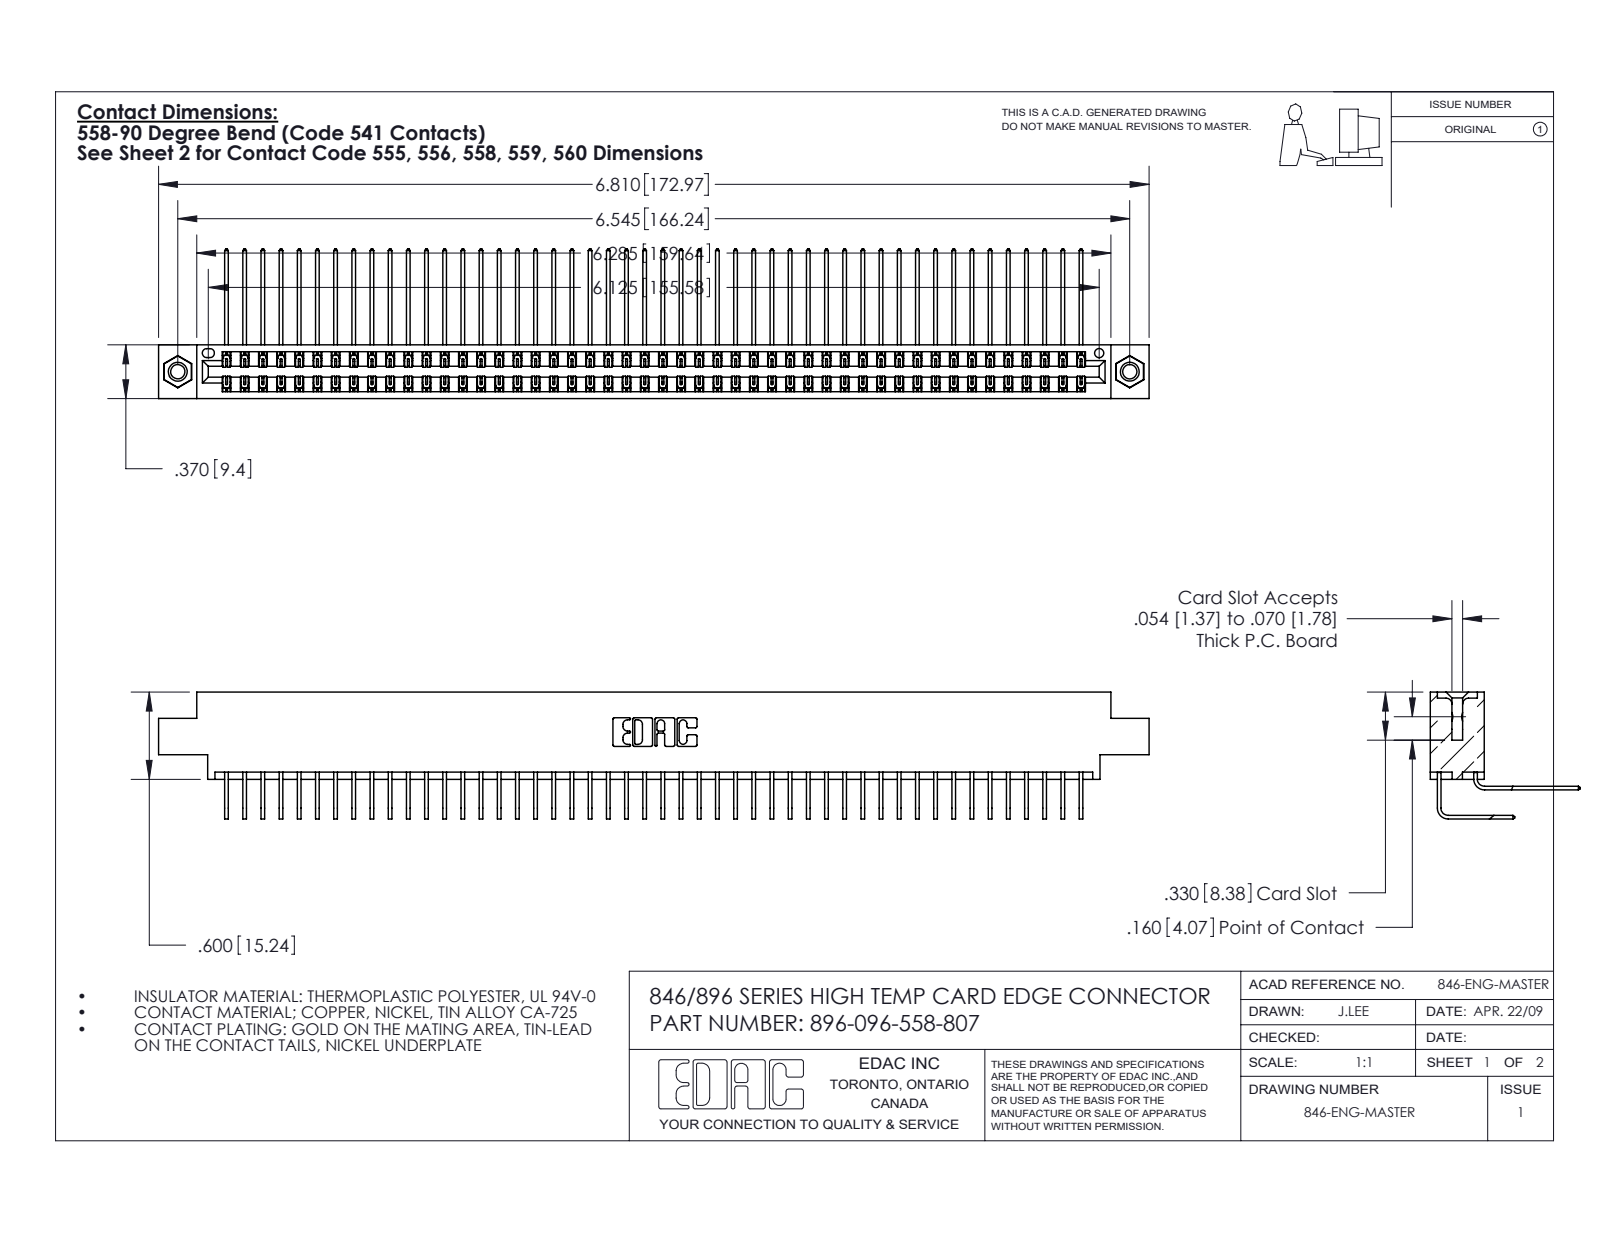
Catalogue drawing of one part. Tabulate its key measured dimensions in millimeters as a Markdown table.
| quantity | value |
| --- | --- |
| part name | 345-250-001_345-250-005-103; 345-292-001_558 Tail - 2; 346 Part_0.170 Offset - 0.156 Dia-TI; 345-292-001_558 559 Tail - 1 (+1 more) |
| STEP written by | SolidWorks 2016 (CONFIG_CONTROL_DESIGN) |
| units | millimeters |
| bodies | 99 solids, 5370 faces (3664 planar, 1690 cylindrical, 16 other) |
| overall size | 173 × 26.2 × 22.2 |
| volume | 17 300 mm³ |
| surface area | 26 740 mm² |
| round holes (diameter × count) | 2.5 × 2, 3.2 × 2, 4 × 2, 1.6 × 1 |
| round bosses / shafts (diameter × count) | 3.9 × 2 |
| partial cylindrical surfaces (radius × count) | 0.2 × 144, 0.3 × 22, 0.2 × 6, 0.8 × 6, 0.7 × 3, 0.4 × 2, 0.6 × 2, 0.6 × 2 |
| main face-to-face distances | 8.2, 1.2, 0.6, 9.4, 6.4, 7.6, 1.8, 7, 5.6, 3.8 |
| hole center spacings | 6.2, 160.9, 166.2 |
